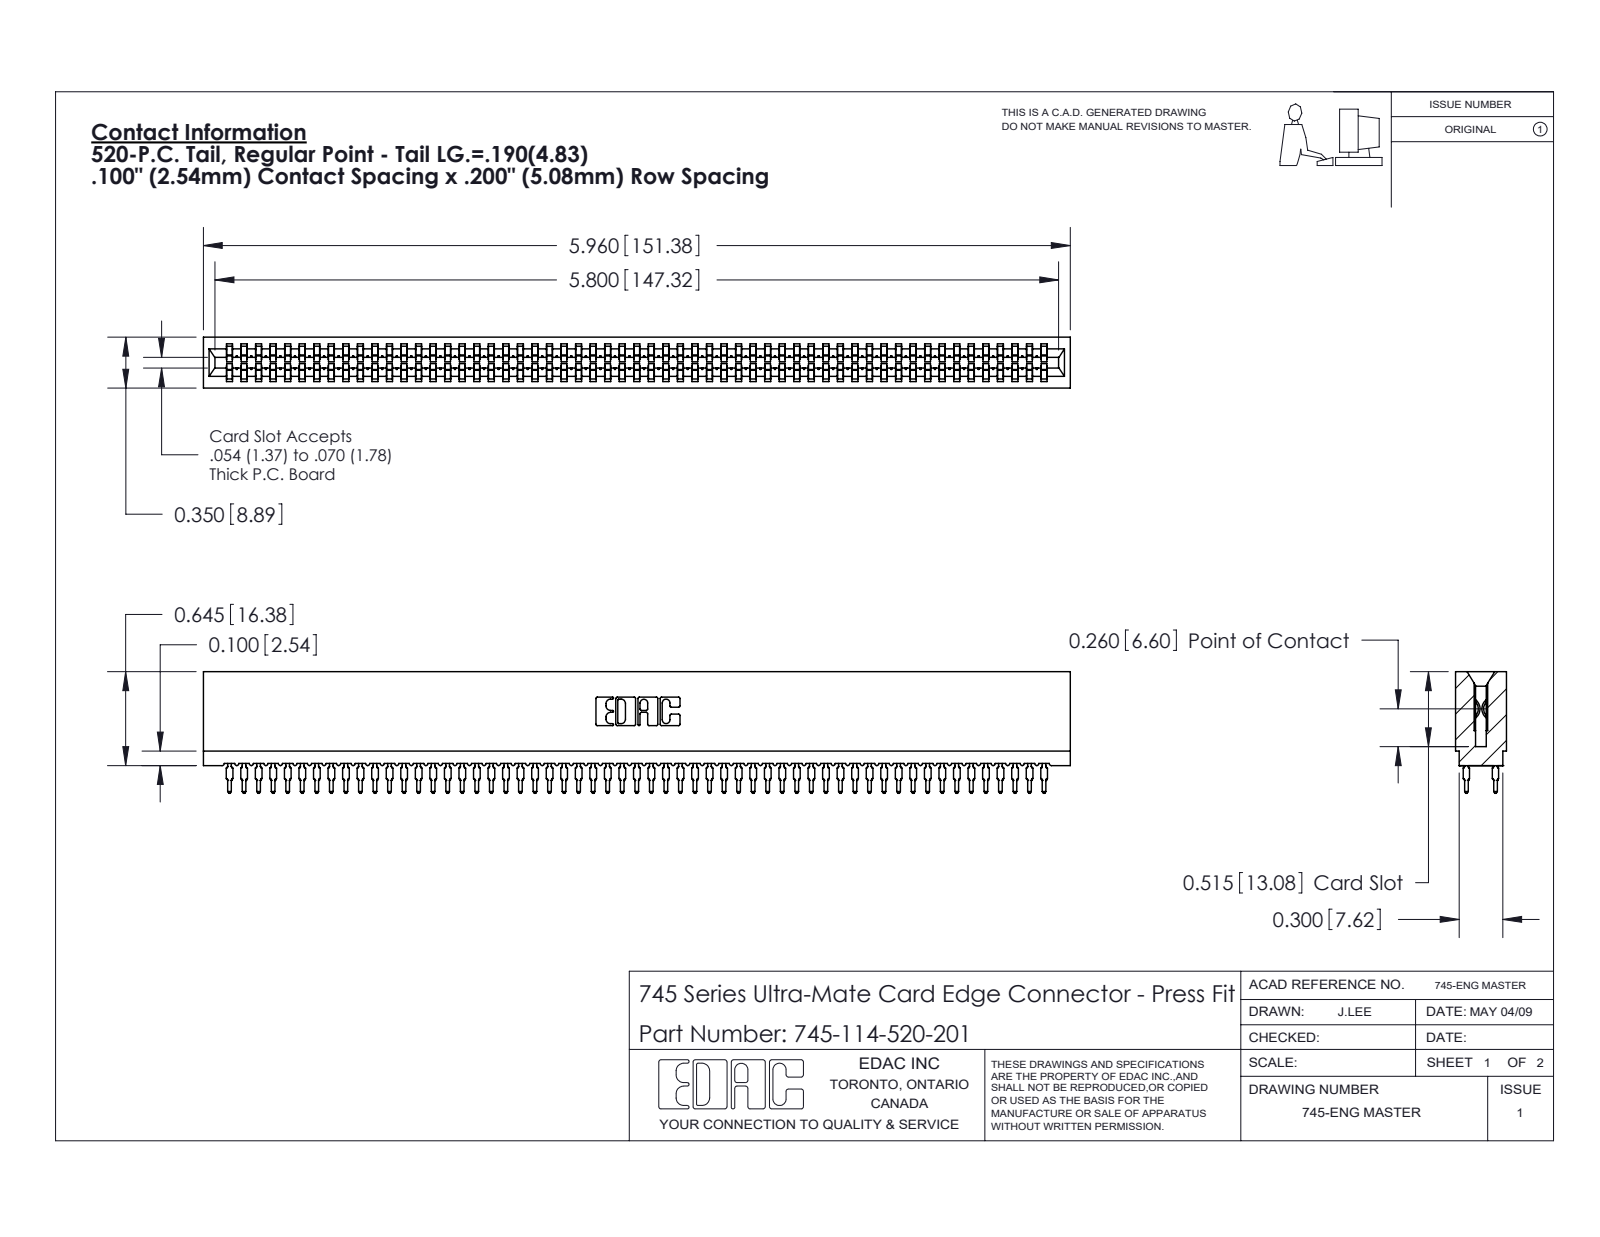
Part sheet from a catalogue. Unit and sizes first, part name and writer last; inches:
Units: inches
Overall size (bounding box): 5.96 × 0.836 × 0.35
Partial cylindrical surfaces — rounded edges, fillets, slot ends (radius × count): R0.021 ×228, R0.015 ×114, R0.01 ×22, R0.005 ×8, R0.011 ×8, R0.007 ×6, R0.031 ×6, R0.026 ×3
Main face-to-face distances: 0.35, 0.063, 0.287, 0.045, 0.305, 0.018, 0.243, 0.138, 0.212, 0.093
Volume: 0.821 in³ · Surface area: 42.1 in²
Bodies: 115 solids, 10298 faces (5299 planar, 2035 cylindrical, 2964 other)
Part name (STEP PRODUCT): 745 Part_Insulator Option - 01; 745-114-520-201; 745-292-001_520
STEP written by: SolidWorks 2020 (CONFIG_CONTROL_DESIGN)
